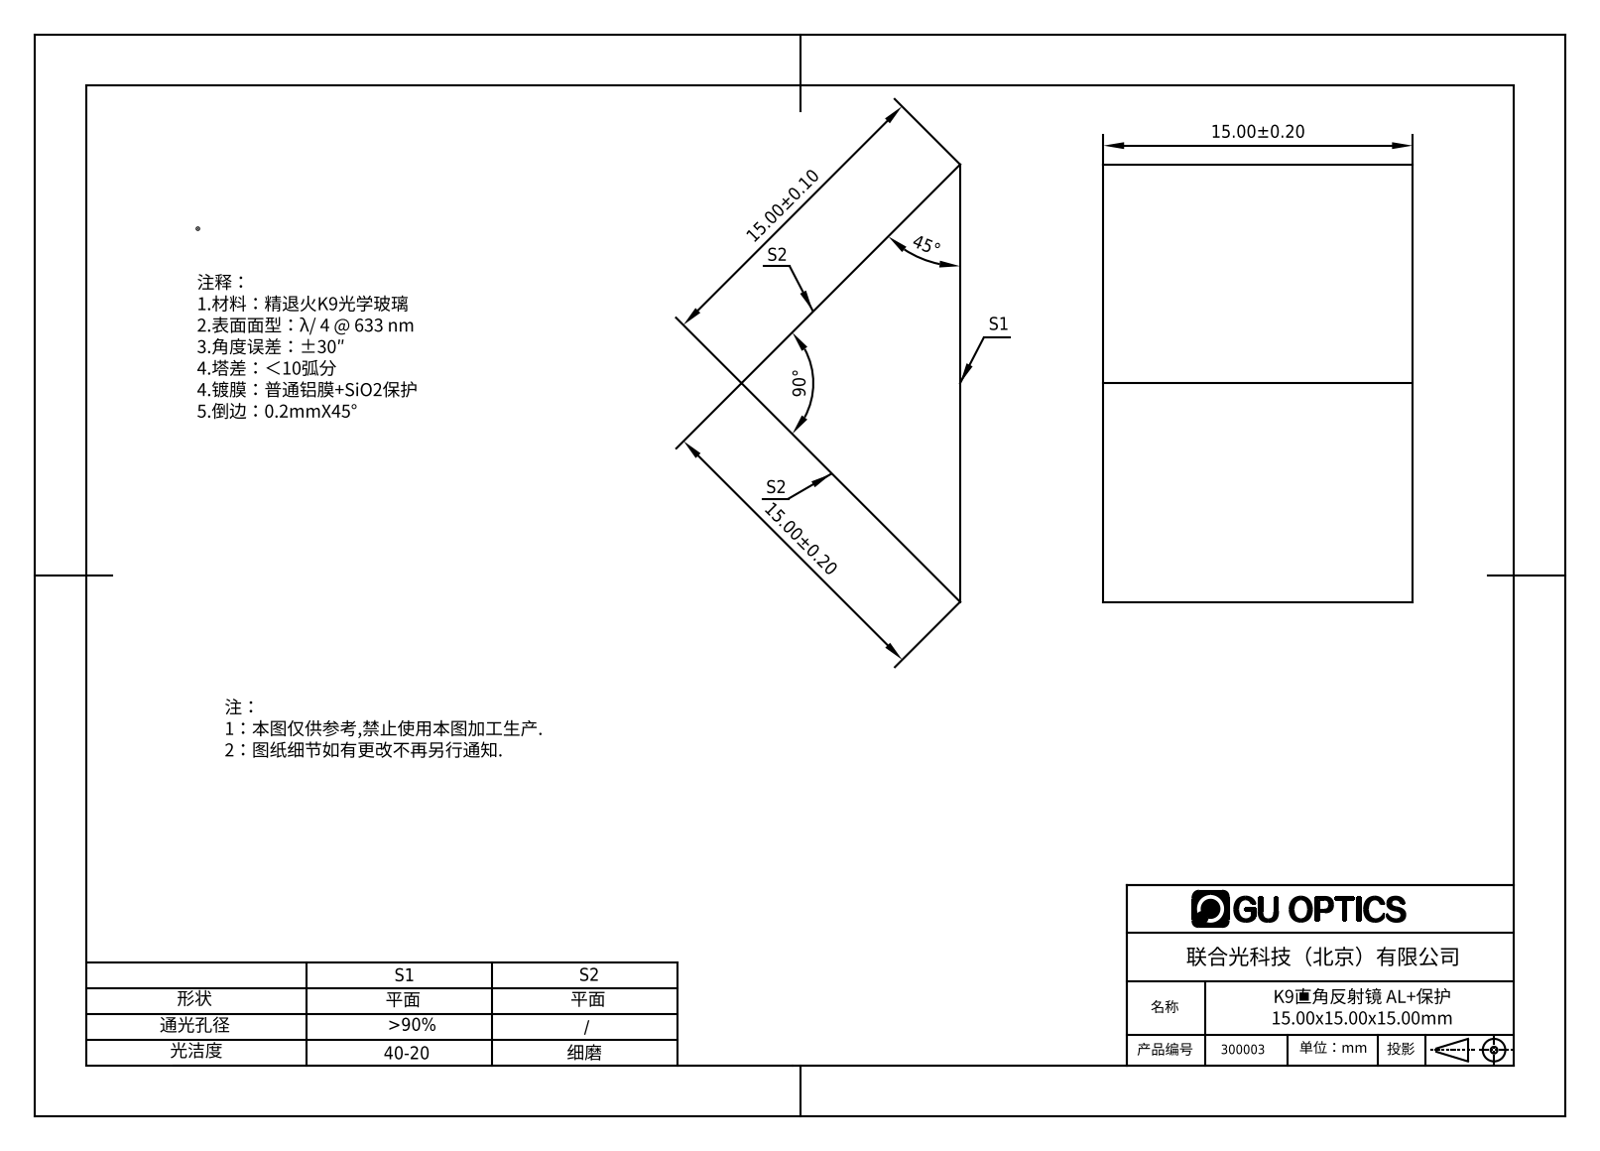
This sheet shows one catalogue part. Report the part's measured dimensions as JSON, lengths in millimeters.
{"part_name": "300003", "step_written_by": "SolidWorks 2016 (AUTOMOTIVE_DESIGN)", "units": "millimeters", "bodies": {"solids": 1, "faces": 5, "planar": 5, "cylindrical": 0, "other": 0}, "overall_size": [21.21, 15, 10.61], "volume_mm3": 1688, "surface_area_mm2": 993, "face_to_face_distances": [15]}
